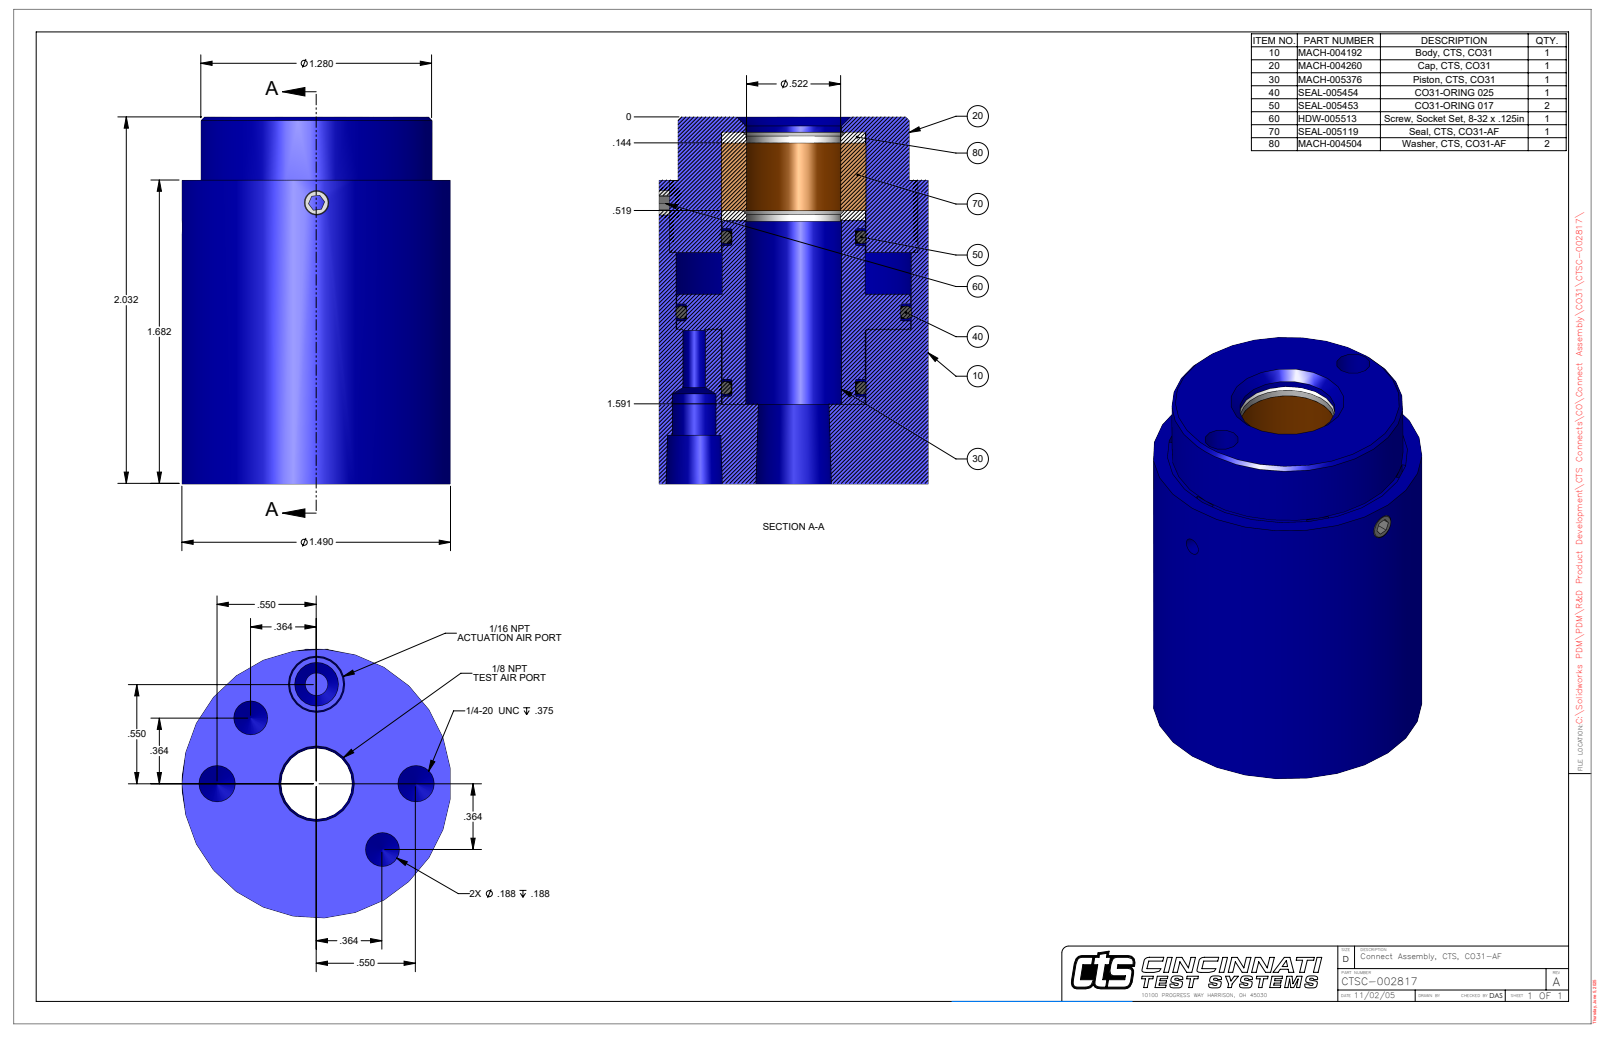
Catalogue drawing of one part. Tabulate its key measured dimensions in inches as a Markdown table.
| quantity | value |
| --- | --- |
| part name | CTSC-002817 |
| STEP written by | SolidWorks 2023 (AUTOMOTIVE_DESIGN) |
| units | inches |
| bodies | 1 solid, 108 faces (52 planar, 38 cylindrical, 18 other) |
| overall size | 2.032 × 1.49 × 1.49 |
| volume | 2.913 in³ |
| surface area | 17.18 in² |
| round holes (diameter × count) | 0.187 × 4, 0.201 × 2, 0.094 × 1, 0.136 × 1, 0.242 × 1, 0.522 × 1, 0.53 × 1, 0.8 × 1, 1.33 × 1 |
| round bosses / shafts (diameter × count) | 1.49 × 1, 1.28 × 1, 0.792 × 1 |
| partial cylindrical surfaces (radius × count) | 0.687 × 1, 0.732 × 1 |
| main face-to-face distances | 2.032, 1.682, 0.35, 0.31, 1.372, 1.722, 0.441, 0.131, 1.241, 1.591 |
| hole center spacings | 0.515, 0.409, 0.55, 0.984, 0.035, 0.394, 0.754, 0.778 |
